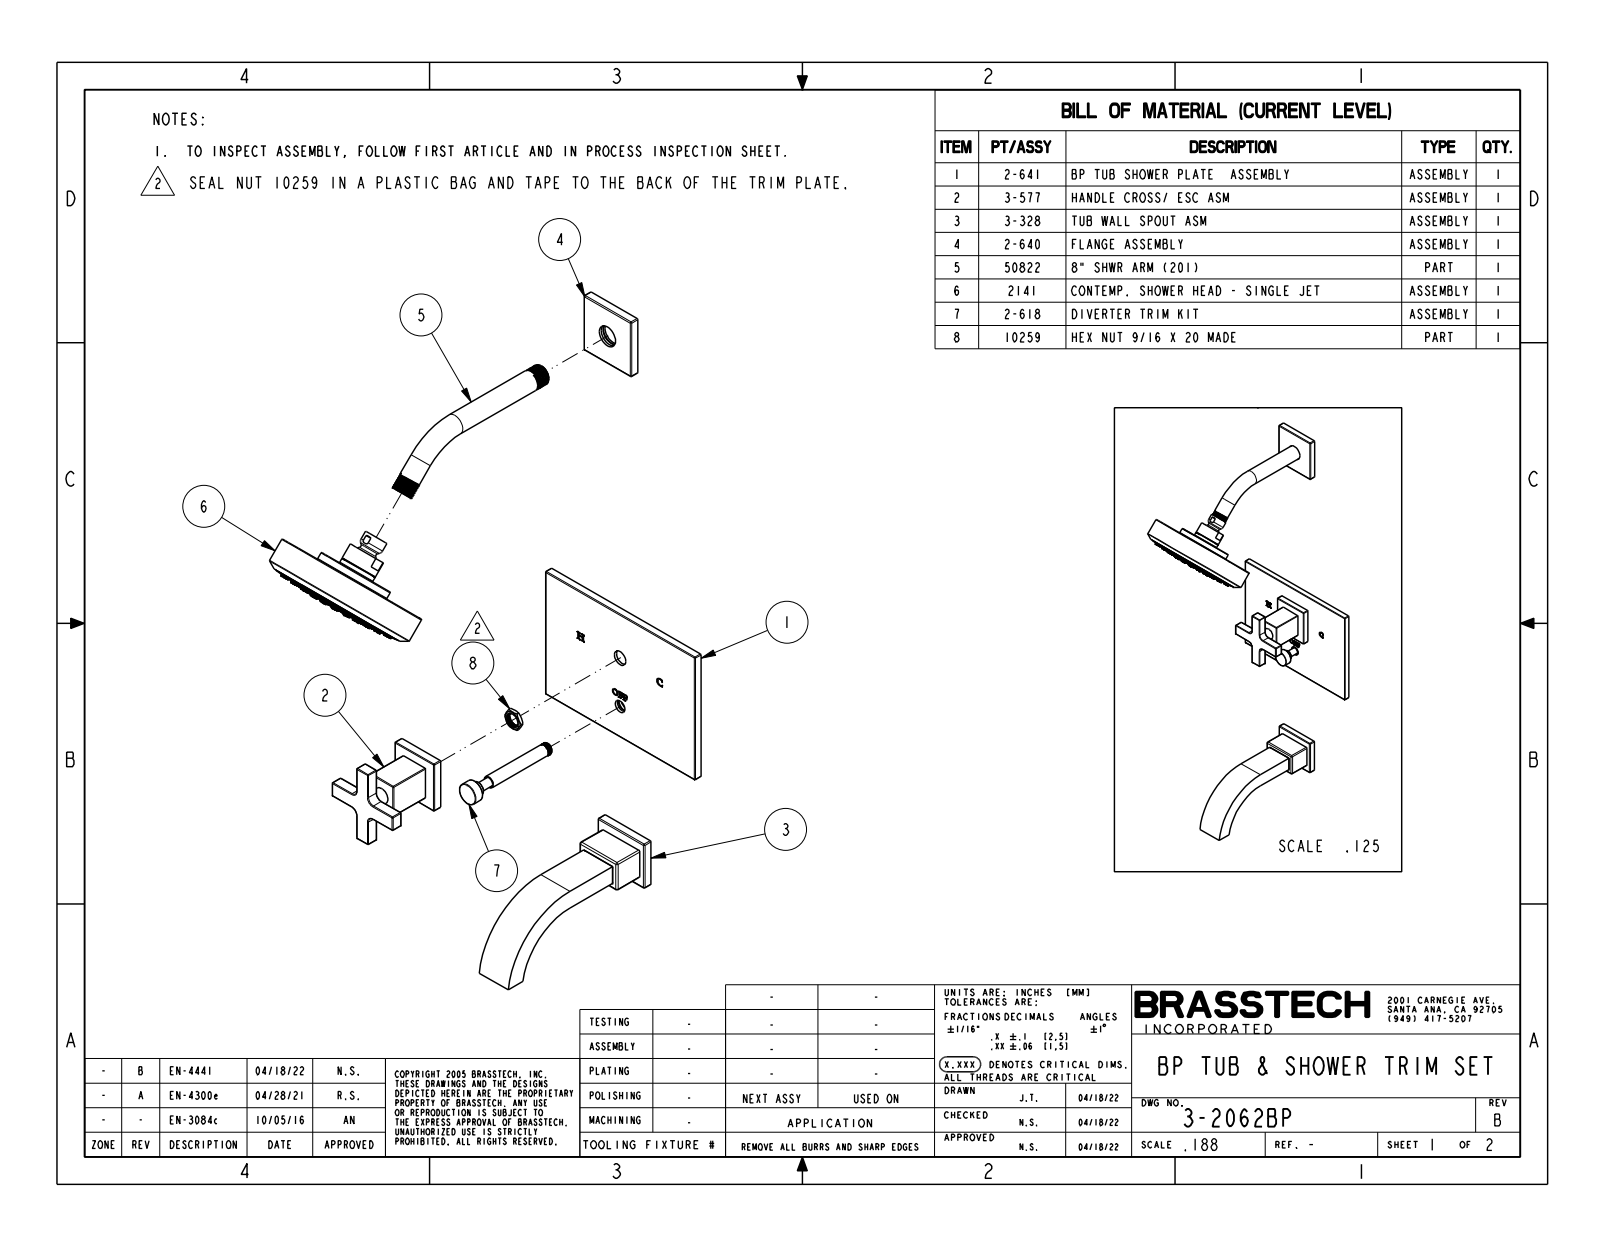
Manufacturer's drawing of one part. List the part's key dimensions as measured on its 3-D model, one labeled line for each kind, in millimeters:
Part name (STEP PRODUCT): 3-2062BP
STEP written by: CREO PARAMETRIC BY PTC INC, 2018400 (CONFIG_CONTROL_DESIGN)
Units: millimetres
Bodies: 3 solids, 1275 faces (200 planar, 302 cylindrical, 773 other)
Overall size (bounding box): 601.5 × 260 × 196.9
Volume: 1 157 000 mm³ · Surface area: 184 600 mm²
Round holes (diameter × count): ⌀1.3 ×90, ⌀5.6 ×1, ⌀133.5 ×1
Round bosses / shafts (diameter × count): ⌀35.6 ×2, ⌀20.7 ×2, ⌀150.1 ×1, ⌀132.6 ×1, ⌀74.2 ×1, ⌀23 ×1, ⌀21.3 ×1, ⌀16.5 ×1
Partial cylindrical surfaces — rounded edges, fillets, slot ends (radius × count): R0.8 ×48, R1 ×16, R1.5 ×8, R6.4 ×4, R62.6 ×1, R81.6 ×1
Main face-to-face distances: 7.9, 8.9, 1, 38.1, 11.4, 7.4, 19.1, 4.3, 33.8, 85.2
Hole centre spacings: 24.9, 35.8, 34.1, 24.9, 10.9, 37.6, 43.1, 12.9
